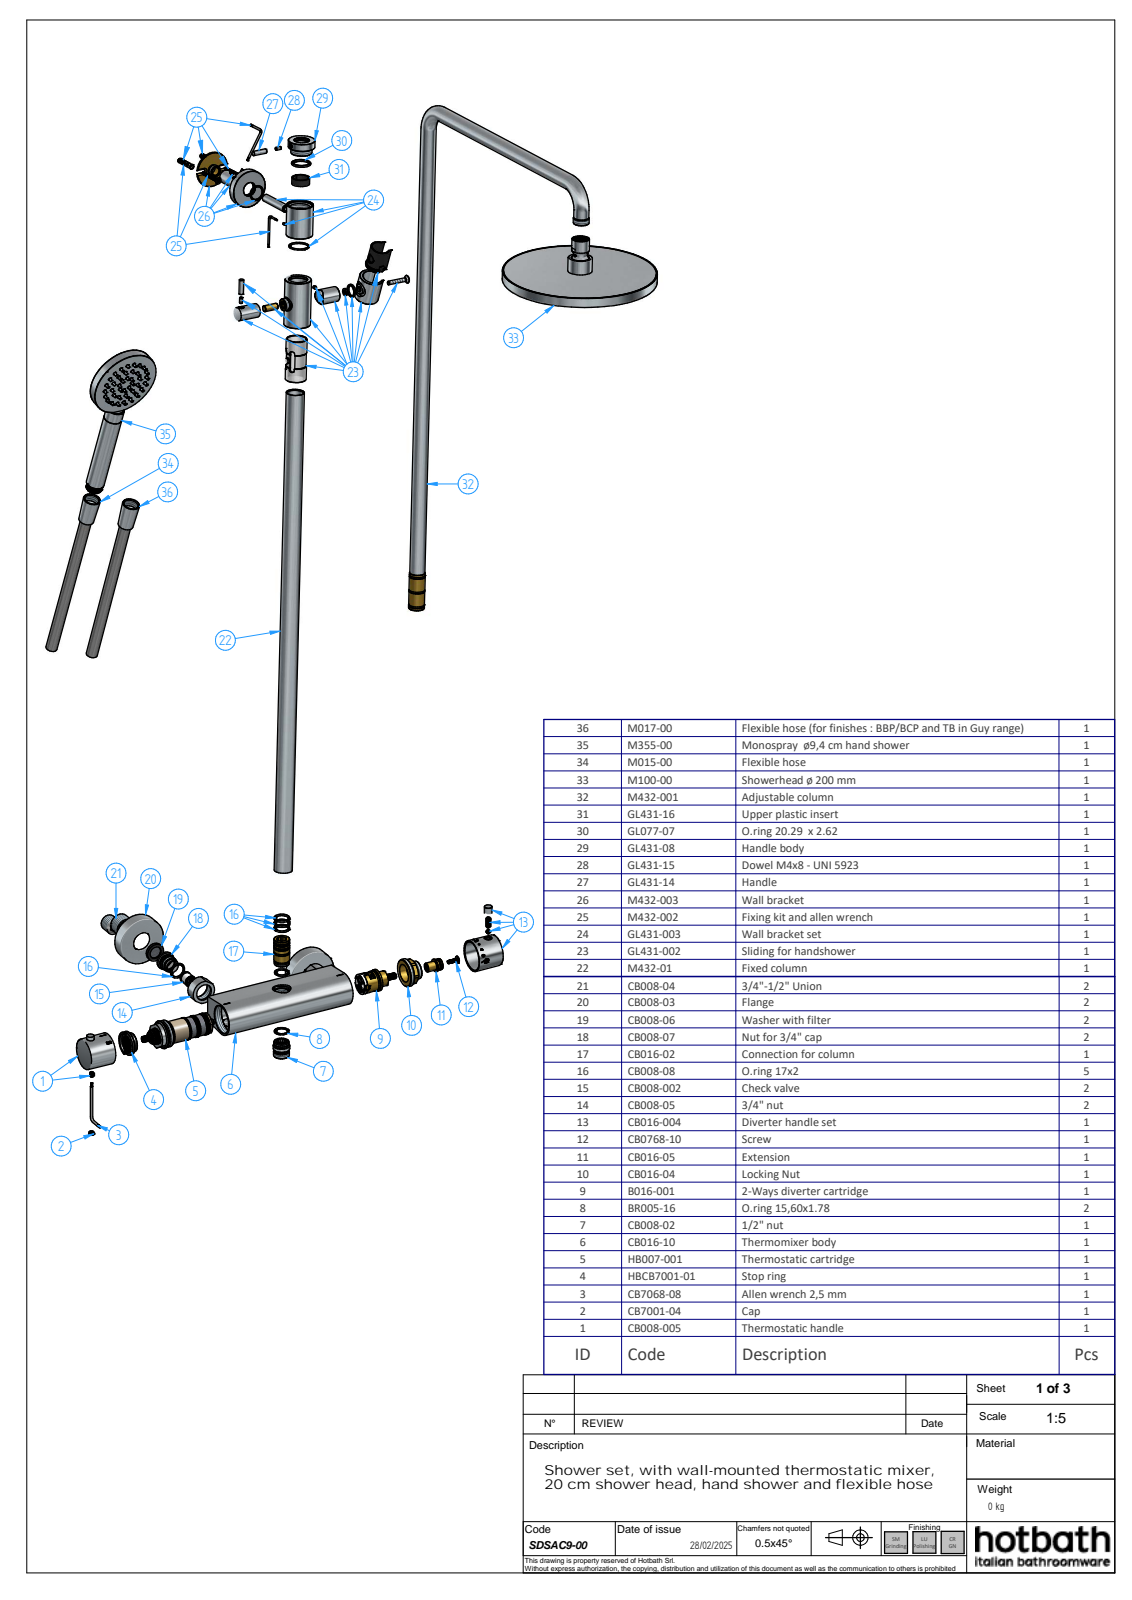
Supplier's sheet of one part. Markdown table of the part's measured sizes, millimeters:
| quantity | value |
| --- | --- |
| part name | SDSAC10-00; M432-00_oa_0; M432-01; GL431-003_oa_1 (+8 more) |
| STEP written by | Solid Edge (AUTOMOTIVE_DESIGN) |
| units | millimeters |
| bodies | 45 solids, 4385 faces (1240 planar, 1073 cylindrical, 2072 other) |
| overall size | 1461.19 × 546.26 × 259.35 |
| volume | 981 643 mm³ |
| surface area | 809 048 mm² |
| round holes (diameter × count) | 4.5 × 127, 1 × 126, 4.4 × 40, 2.4 × 10, 2.5 × 7, 18.5 × 6, 3.24 × 5, 7 × 5, 3.3 × 4, 4.8 × 4, 8 × 4, 16.5 × 4 |
| round bosses / shafts (diameter × count) | 20 × 4, 18 × 4, 7 × 4, 24 × 3, 10 × 3, 6 × 3, 4 × 3, 64 × 2 |
| partial cylindrical surfaces (radius × count) | 2 × 113, 0.2 × 56, 0.5 × 11, 2 × 10, 9 × 10, 6 × 5, 0.46 × 4, 3 × 4 |
| main face-to-face distances | 4, 3, 1, 12.5, 8.5, 6.4, 11.5, 6.1, 5.1, 5 |
| hole center spacings | 12, 9.77, 18.52, 10.01, 47.15, 9, 28.53, 29.06 |
